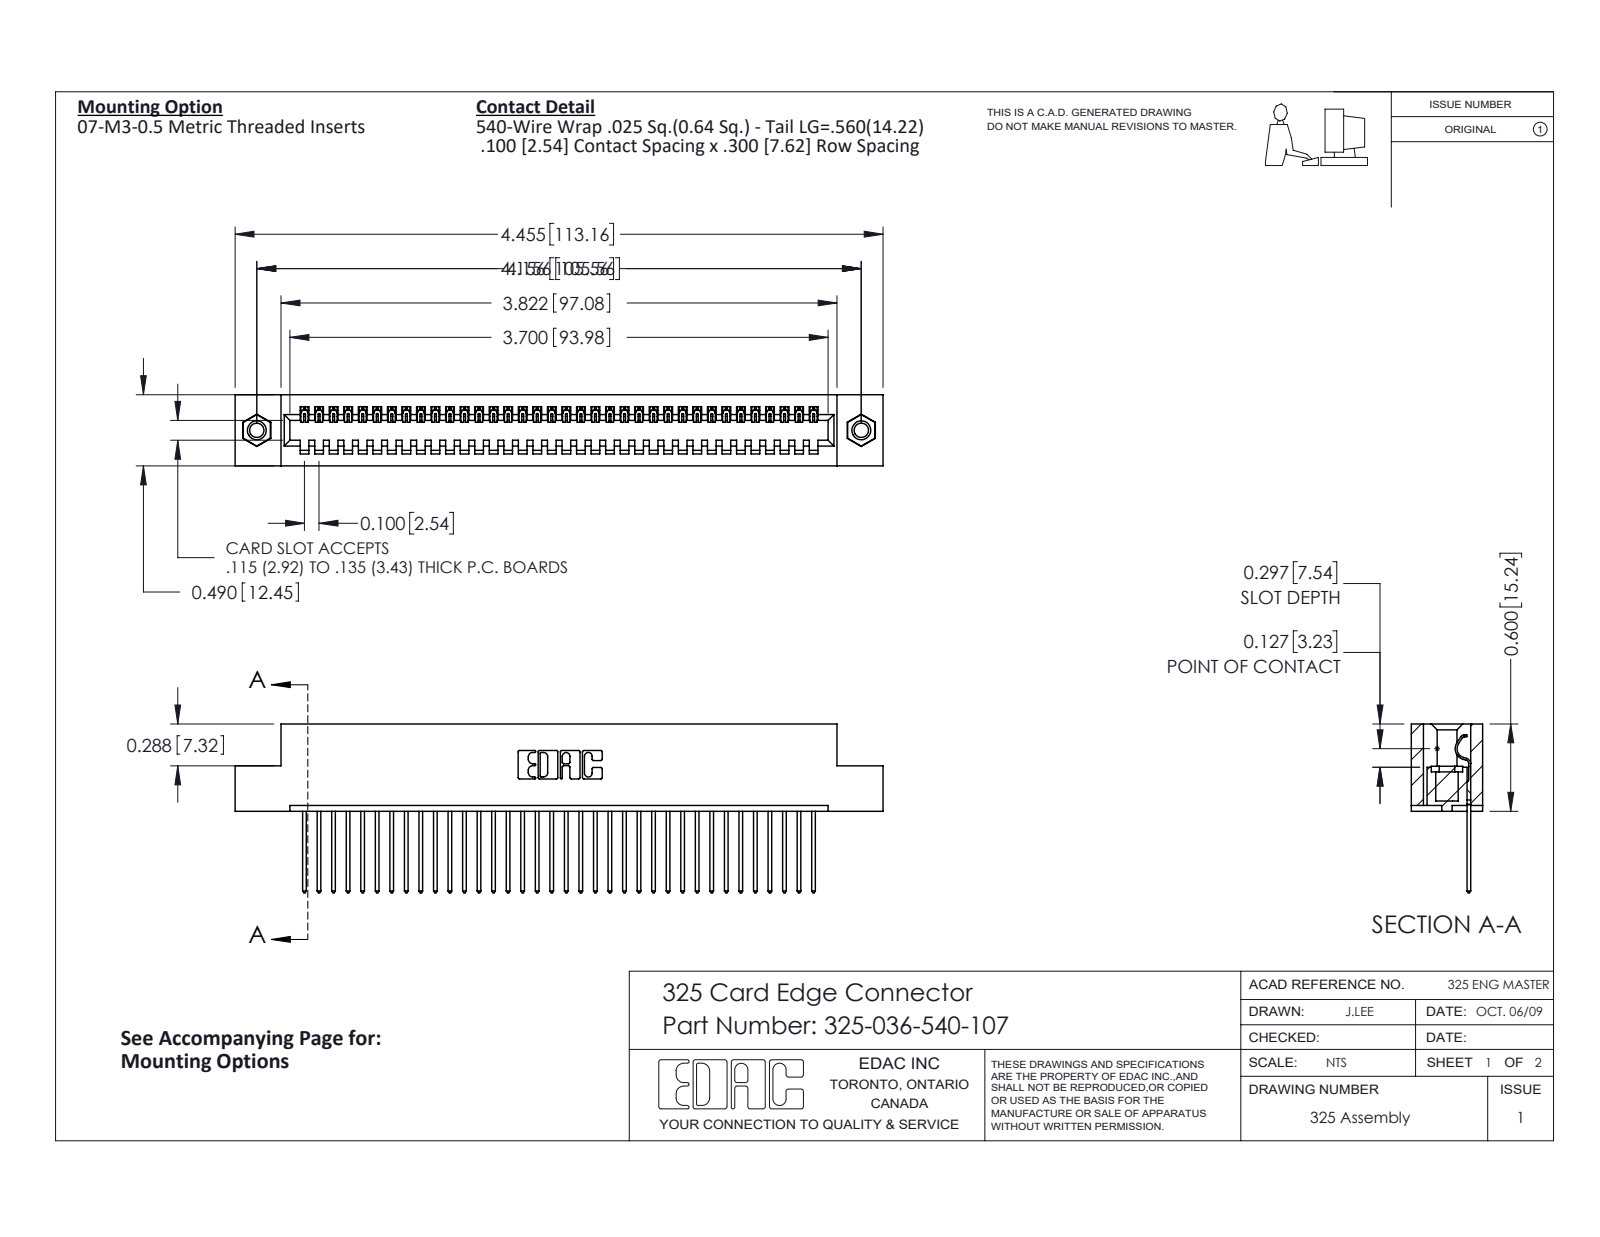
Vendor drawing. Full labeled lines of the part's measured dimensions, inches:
Part name (STEP PRODUCT): 325 Part_TI; 325-036-540-107; 325-292-001_325-293-140; 345-250-001_345-250-005-103
STEP written by: SolidWorks 2016 (CONFIG_CONTROL_DESIGN)
Units: inches
Bodies: 39 solids, 2262 faces (1614 planar, 632 cylindrical, 16 other)
Overall size (bounding box): 4.455 × 1.16 × 0.49
Volume: 0.876 in³ · Surface area: 24.75 in²
Round holes (diameter × count): ⌀0.098 ×2, ⌀0.125 ×2, ⌀0.16 ×2
Round bosses / shafts (diameter × count): ⌀0.155 ×2
Partial cylindrical surfaces — rounded edges, fillets, slot ends (radius × count): R0.006 ×72, R0.01 ×72, R0.01 ×22, R0.007 ×6, R0.031 ×6, R0.026 ×3, R0.014 ×1, R0.022 ×1
Main face-to-face distances: 0.083, 0.407, 0.49, 0.3, 0.107, 0.383, 0.025, 0.325, 0.56, 0.04
Hole centre spacings: 4.156
